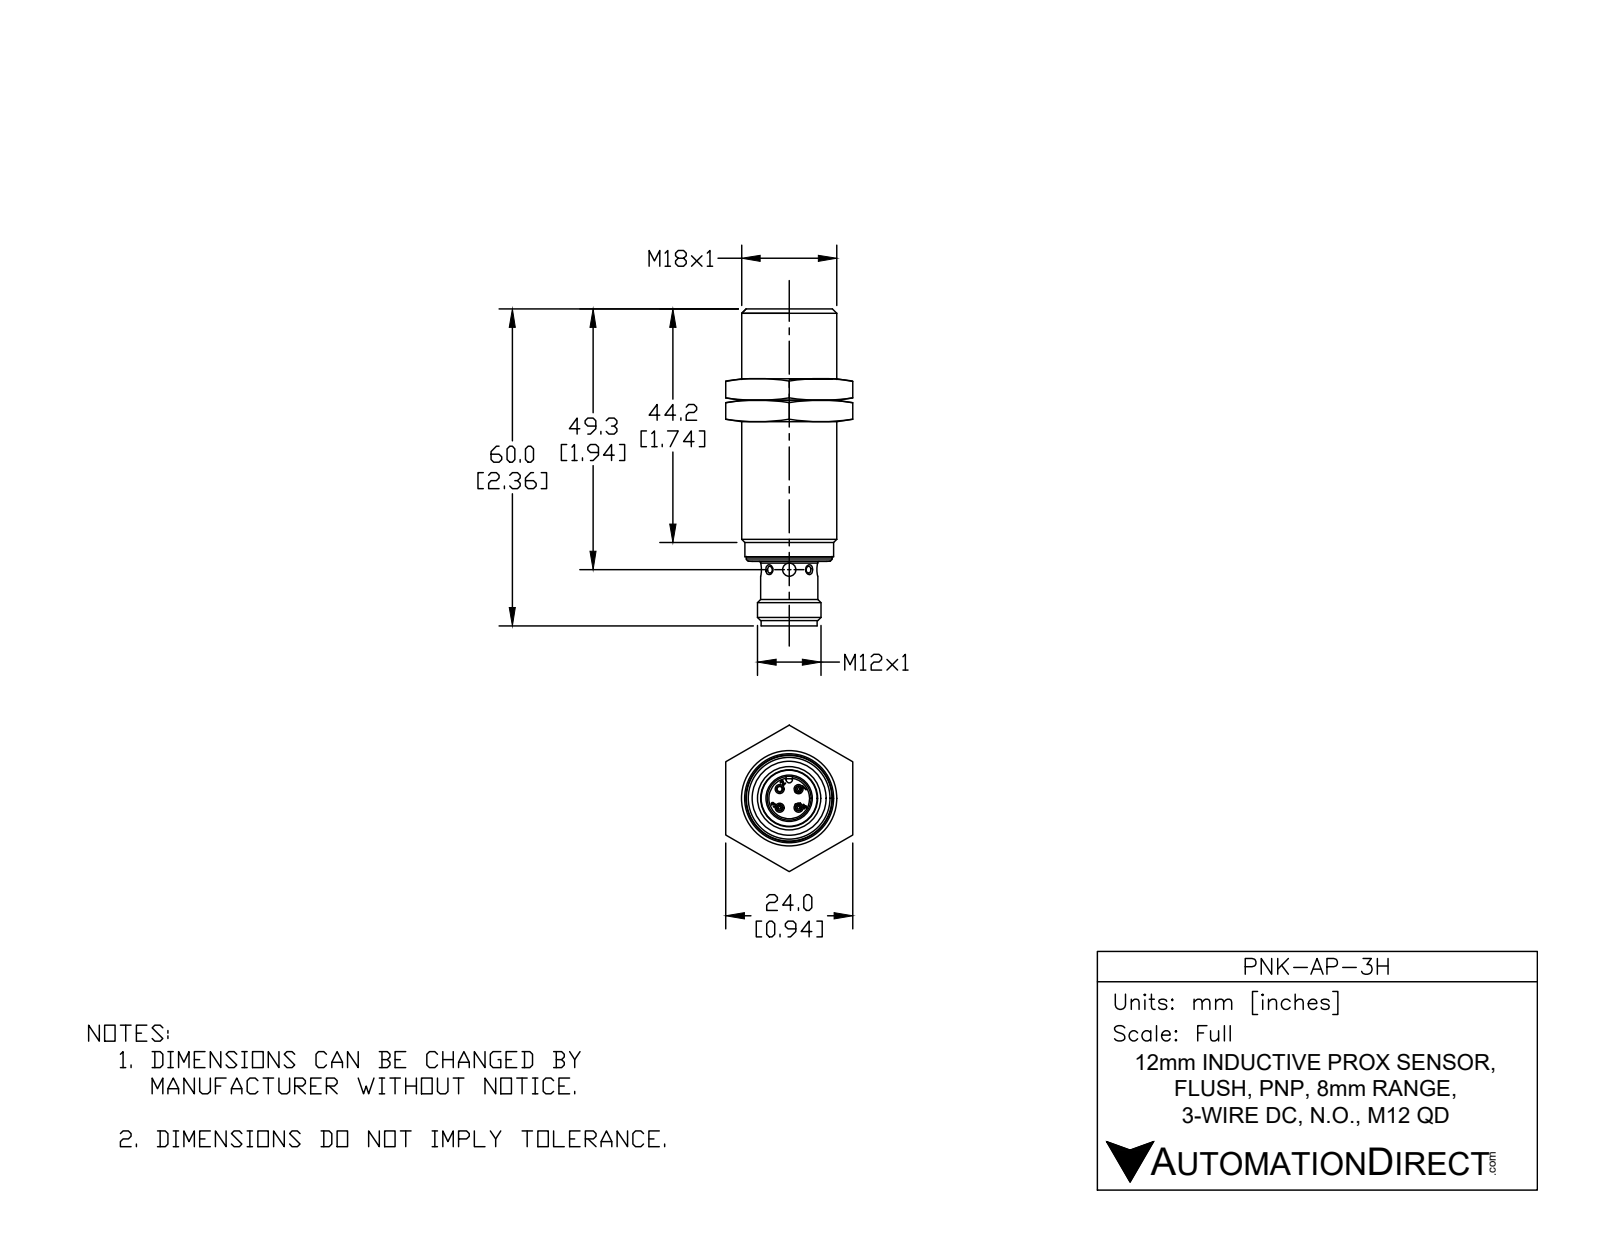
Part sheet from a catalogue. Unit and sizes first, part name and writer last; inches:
Units: inches
Overall size (bounding box): 2.362 × 0.709 × 0.709
Round holes (diameter × count): ⌀0.043 ×3, ⌀0.04 ×2, ⌀0.098 ×2, ⌀0.038 ×1, ⌀0.04 ×1, ⌀0.327 ×1, ⌀0.394 ×1, ⌀0.618 ×1, ⌀0.634 ×1
Round bosses / shafts (diameter × count): ⌀0.039 ×9, ⌀0.709 ×1, ⌀0.654 ×1, ⌀0.638 ×1, ⌀0.633 ×1, ⌀0.616 ×1, ⌀0.608 ×1, ⌀0.599 ×1
Partial cylindrical surfaces — rounded edges, fillets, slot ends (radius × count): R0.004 ×38, R0.024 ×1, R0.031 ×1, R0.161 ×1
Main face-to-face distances: 0.039, 0.022, 0.018, 1.87, 1.882, 1.86, 1.843, 1.848, 1.831, 2.323
Hole centre spacings: 0.098, 0.139, 0.197
Volume: 0.746 in³ · Surface area: 14.66 in²
Bodies: 1 solid, 1142 faces (751 planar, 150 cylindrical, 241 other)
Part name (STEP PRODUCT): PNK-AP-3H
STEP written by: SolidWorks 2017 (AUTOMOTIVE_DESIGN)
